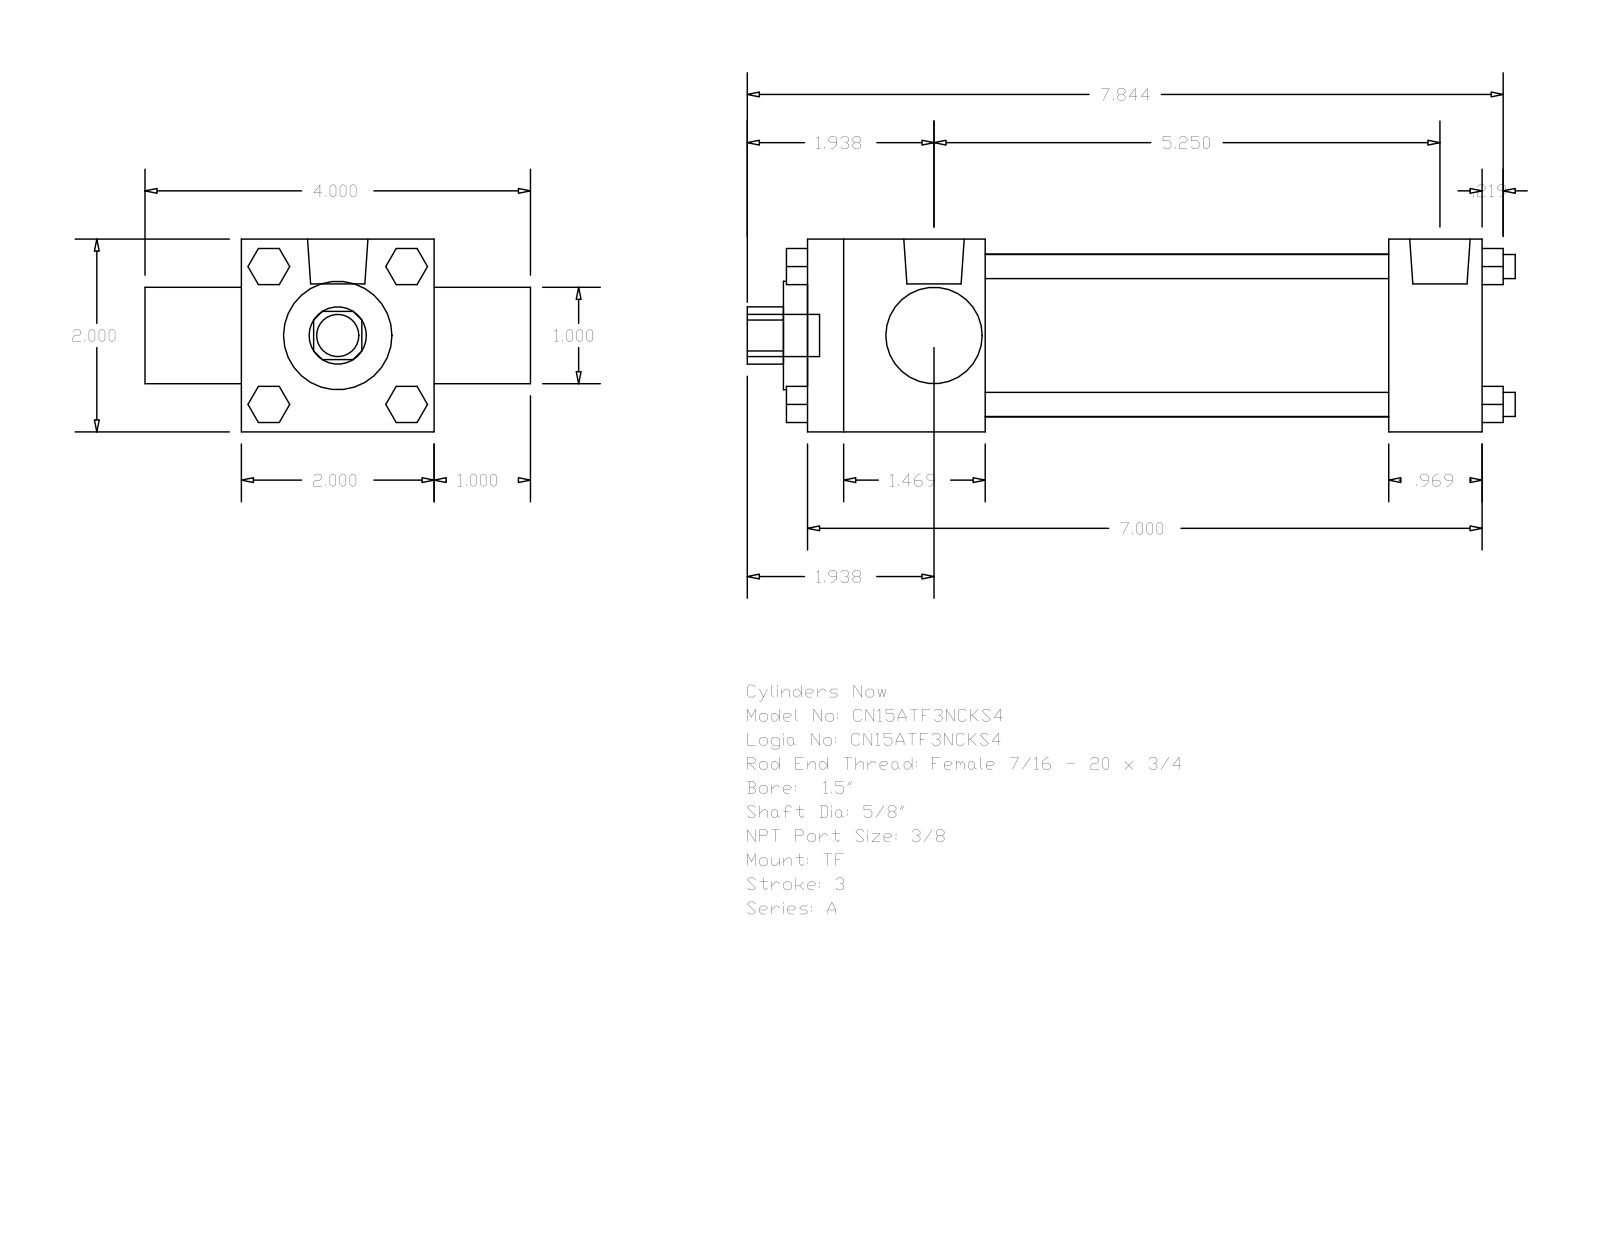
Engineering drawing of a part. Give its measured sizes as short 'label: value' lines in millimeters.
name: A_TF__0150_0.625
written by: GSSL Pune (CONFIG_CONTROL_DESIGN)
unit: mm
bodies: 0 solids, 120 faces (92 planar, 28 cylindrical, 0 other)
size: 202.41 × 101.6 × 50.8
holes: 1× ⌀15.88, 1× ⌀25.4, 1× ⌀28.57, 1× ⌀42.93
bosses: 4× ⌀6.35, 3× ⌀5.56, 2× ⌀15.93, 1× ⌀11.11
rounds: 1× R7.54
face distances: 50.8, 177.8, 25.4, 76.2, 46.83, 153.19, 106.36, 130.97, 24.61, 9.52
